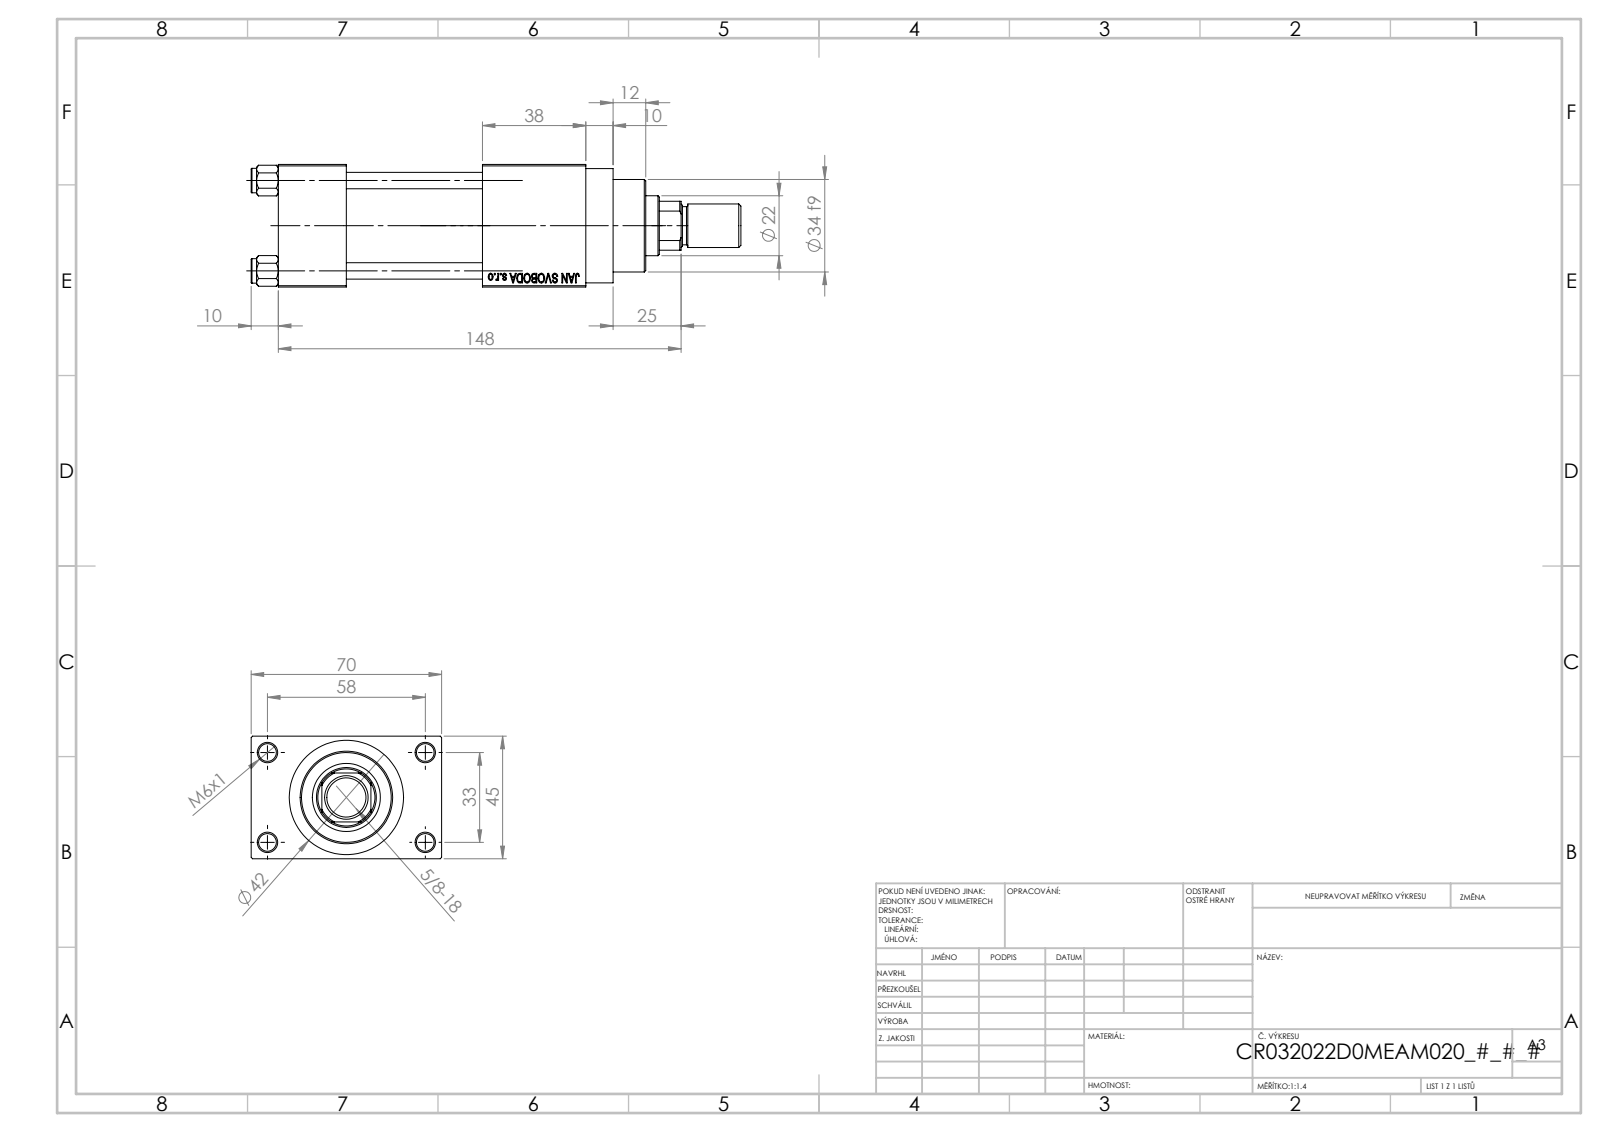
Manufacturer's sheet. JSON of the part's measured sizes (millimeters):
{"part_name": "ROD_END_AH; NUT_M5_D; V215_VC_A; V215CR_VCP_D (+2 more)", "step_written_by": "SolidWorks 2019 (CONFIG_CONTROL_DESIGN)", "units": "millimeters", "bodies": {"solids": 12, "faces": 1117, "planar": 500, "cylindrical": 93, "other": 524}, "overall_size": [180, 70, 45], "volume_mm3": 248936, "surface_area_mm2": 80995, "round_holes": [[6, 4], [6.5, 4], [7, 2], [13.16, 2], [20, 2], [10.5, 1], [22, 1], [24, 1], [25, 1], [32, 1], [33, 1]], "round_bosses_or_shafts": [[9, 4], [42, 1], [38, 1], [34, 1], [16, 1], [14, 1]], "partial_cylinders_radius": [[10.5, 1]], "face_to_face_distances": [45, 25, 12.5, 57.5, 50, 75, 88, 70, 38, 113], "hole_center_spacings": [12.4, 23.48, 33.2, 33.37, 35.35, 45.6, 56.35, 33]}
